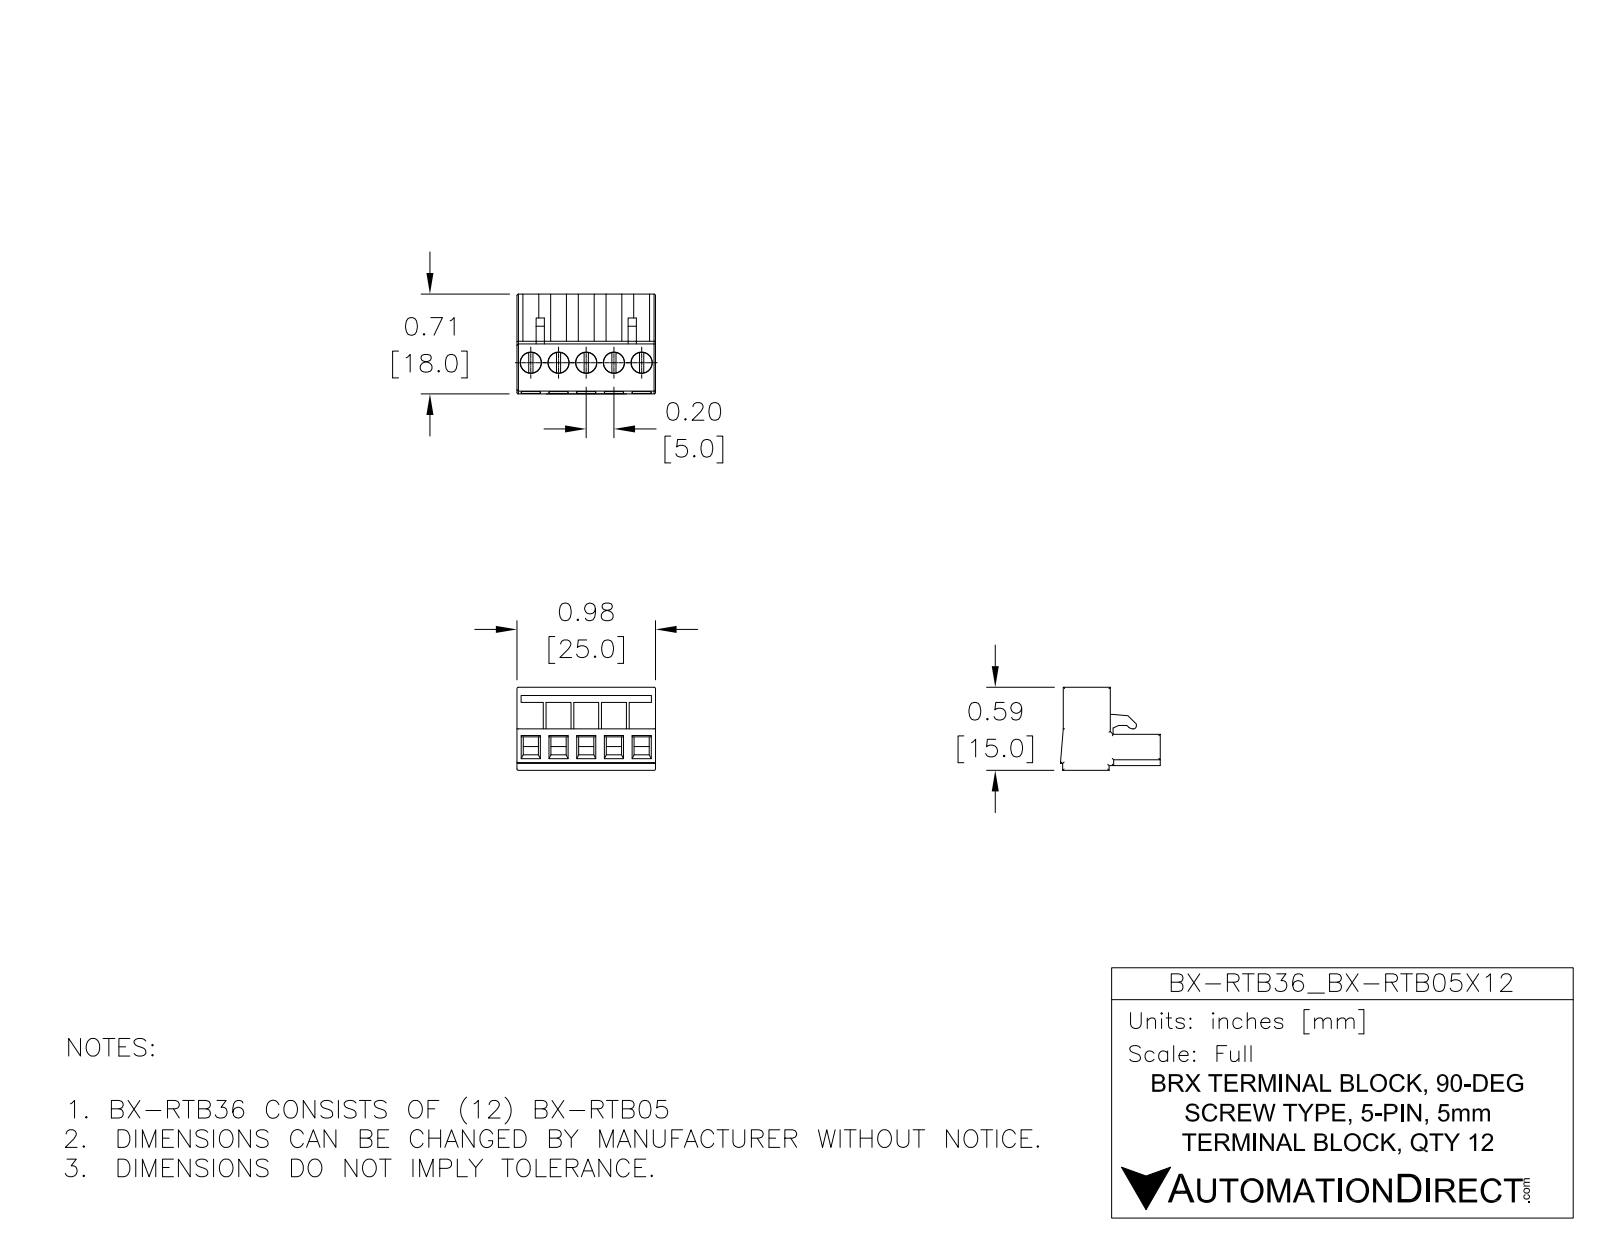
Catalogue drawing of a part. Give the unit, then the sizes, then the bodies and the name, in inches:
Units: inches
Overall size (bounding box): 8.453 × 1.591 × 0.709
Round holes (diameter × count): ⌀0.063 ×60, ⌀0.124 ×60, ⌀0.152 ×30
Round bosses / shafts (diameter × count): ⌀0.148 ×30
Partial cylindrical surfaces — rounded edges, fillets, slot ends (radius × count): R0.01 ×266, R0.099 ×60, R0.02 ×2, R0.039 ×2
Main face-to-face distances: 1, 0.335, 1.484, 4.5, 0.984, 0.591, 0.224, 0.366, 0.256, 5.984
Hole centre spacings: 0.197, 0.394, 1.484, 4.5, 0.591, 1.287, 1.681, 4.303
Volume: 2.797 in³ · Surface area: 56.79 in²
Bodies: 12 solids, 3480 faces (2376 planar, 984 cylindrical, 120 other)
Part name (STEP PRODUCT): BX-RTB36
STEP written by: SolidWorks 2017 (AUTOMOTIVE_DESIGN)
